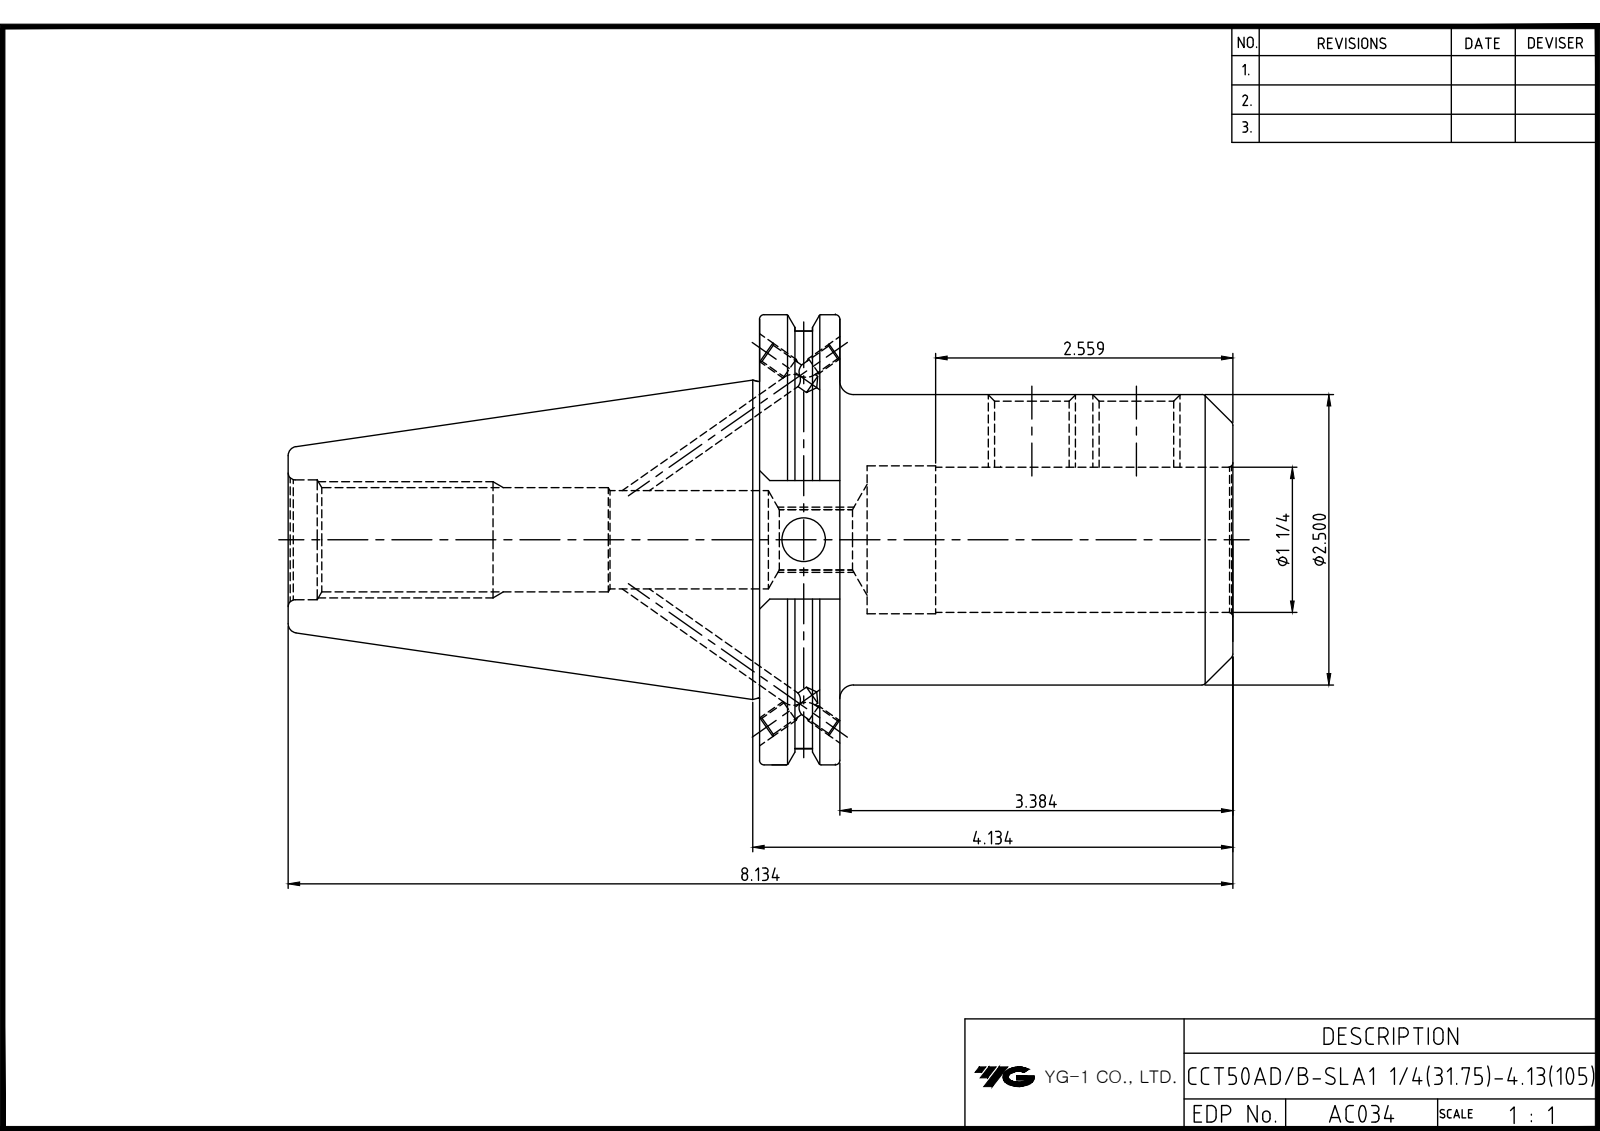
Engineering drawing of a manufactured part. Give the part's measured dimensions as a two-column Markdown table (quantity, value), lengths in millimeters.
| quantity | value |
| --- | --- |
| part name | LO-CCT50ADB-SLA31.75-105 |
| STEP written by | Autodesk Inventor 2025 (AUTOMOTIVE_DESIGN) |
| units | millimeters |
| bodies | 1 solid, 91 faces (36 planar, 29 cylindrical, 26 other) |
| overall size | 206.6 × 98.42 × 94.69 |
| volume | 523 917 mm³ |
| surface area | 70 770 mm² |
| round holes (diameter × count) | 4.13 × 4, 5 × 4, 17.32 × 2, 9.53 × 1, 12.57 × 1, 21.5 × 1, 21.97 × 1, 26.2 × 1, 31.75 × 1, 32.95 × 1 |
| round bosses / shafts (diameter × count) | 98.42 × 1, 91.29 × 1, 69.25 × 1, 63.5 × 1 |
| main face-to-face distances | 17.55, 103.5, 85.95, 103.1, 23.5, 5.95, 80, 120.65, 126.6, 206.6 |
| hole center spacings | 58.74, 22.86 |
